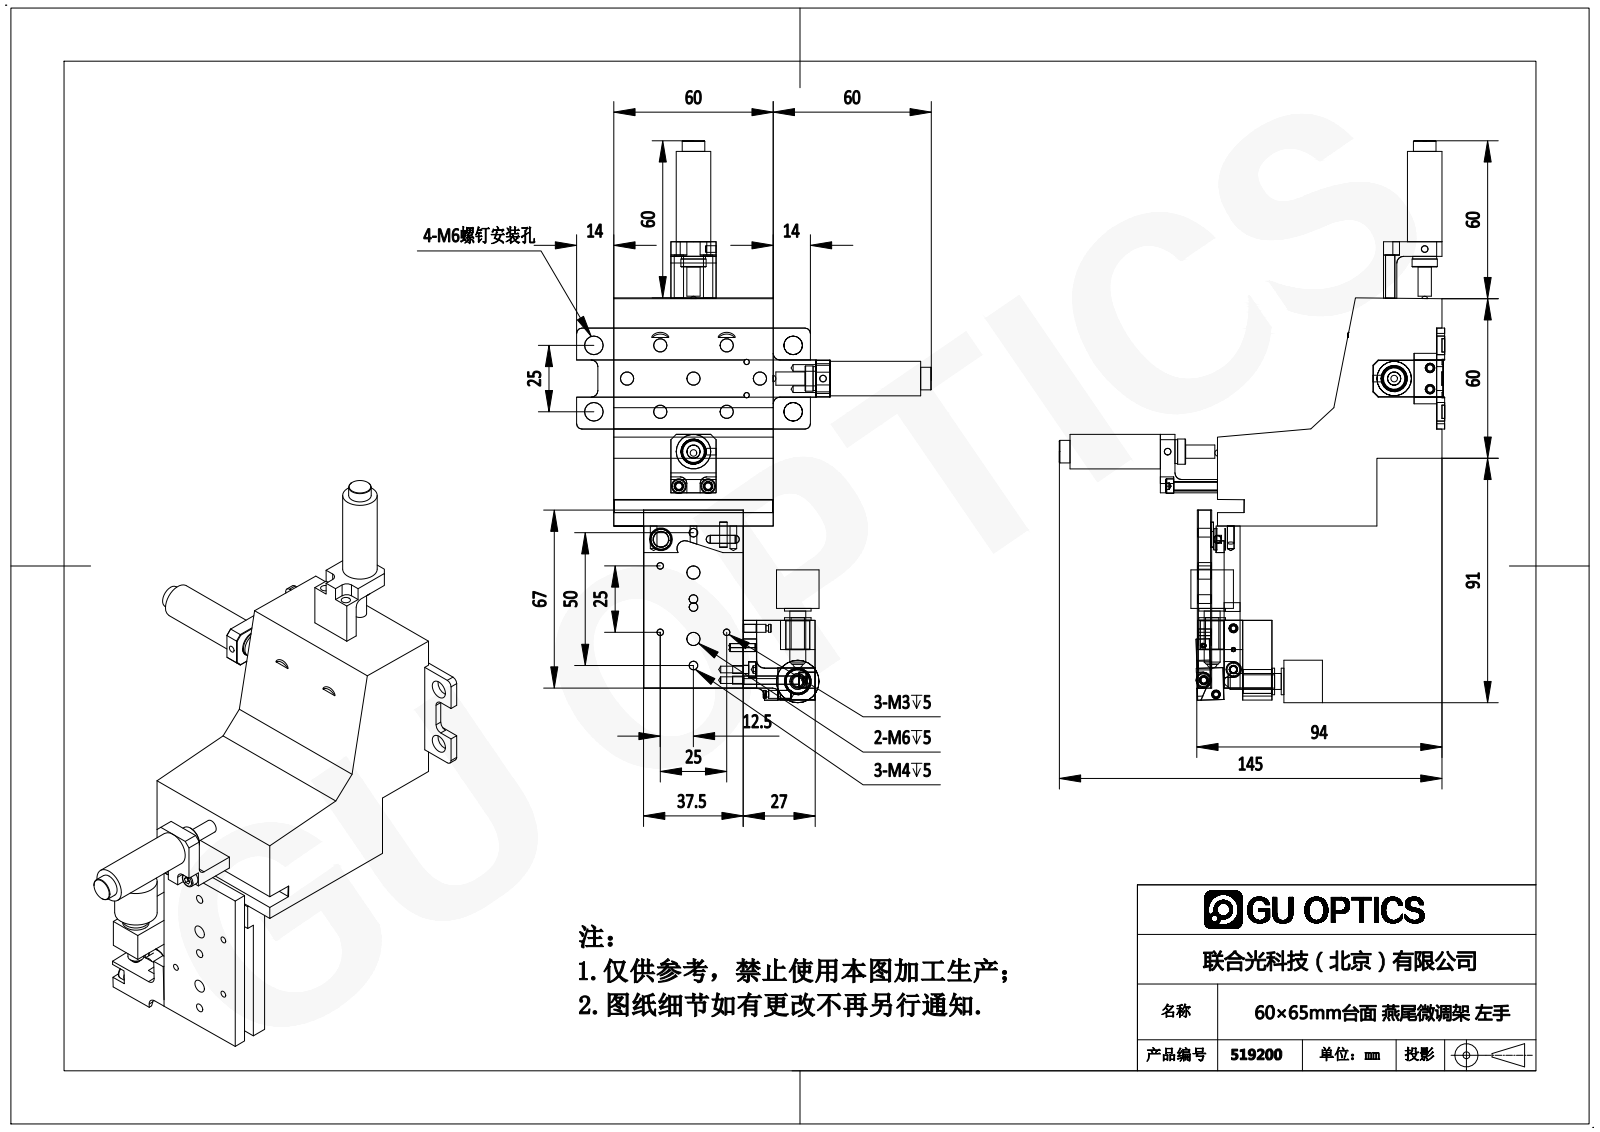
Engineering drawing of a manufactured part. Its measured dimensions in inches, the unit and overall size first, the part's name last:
Units: inches
Overall size (bounding box): 8.327 × 5.709 × 5.256
Round holes (diameter × count): ⌀0.197 ×11, ⌀0.098 ×10, ⌀0.126 ×4, ⌀0.13 ×4, ⌀0.276 ×4, ⌀0.059 ×3, ⌀0.081 ×2, ⌀0.118 ×2, ⌀0.138 ×2, ⌀0.354 ×2, ⌀0.236 ×1
Round bosses / shafts (diameter × count): ⌀0.118 ×5, ⌀0.217 ×4, ⌀0.512 ×3, ⌀0.374 ×3, ⌀0.354 ×3, ⌀0.335 ×3, ⌀0.197 ×3, ⌀0.098 ×3
Partial cylindrical surfaces — rounded edges, fillets, slot ends (radius × count): R0.098 ×10, R0.118 ×7, R0.079 ×4, R0.059 ×3, R0.039 ×1
Main face-to-face distances: 2.362, 1.004, 2.992, 0.02, 3.268, 0.098, 0.039, 0.196, 0.236, 0.335
Hole centre spacings: 0.696, 0.984, 1.556, 1.392, 1.969, 0.512, 2.201, 2.509
Volume: 20.2 in³ · Surface area: 105.2 in²
Bodies: 31 solids, 619 faces (264 planar, 230 cylindrical, 125 other)
Part name (STEP PRODUCT): 519200
STEP written by: SolidWorks 2016 (AUTOMOTIVE_DESIGN)
